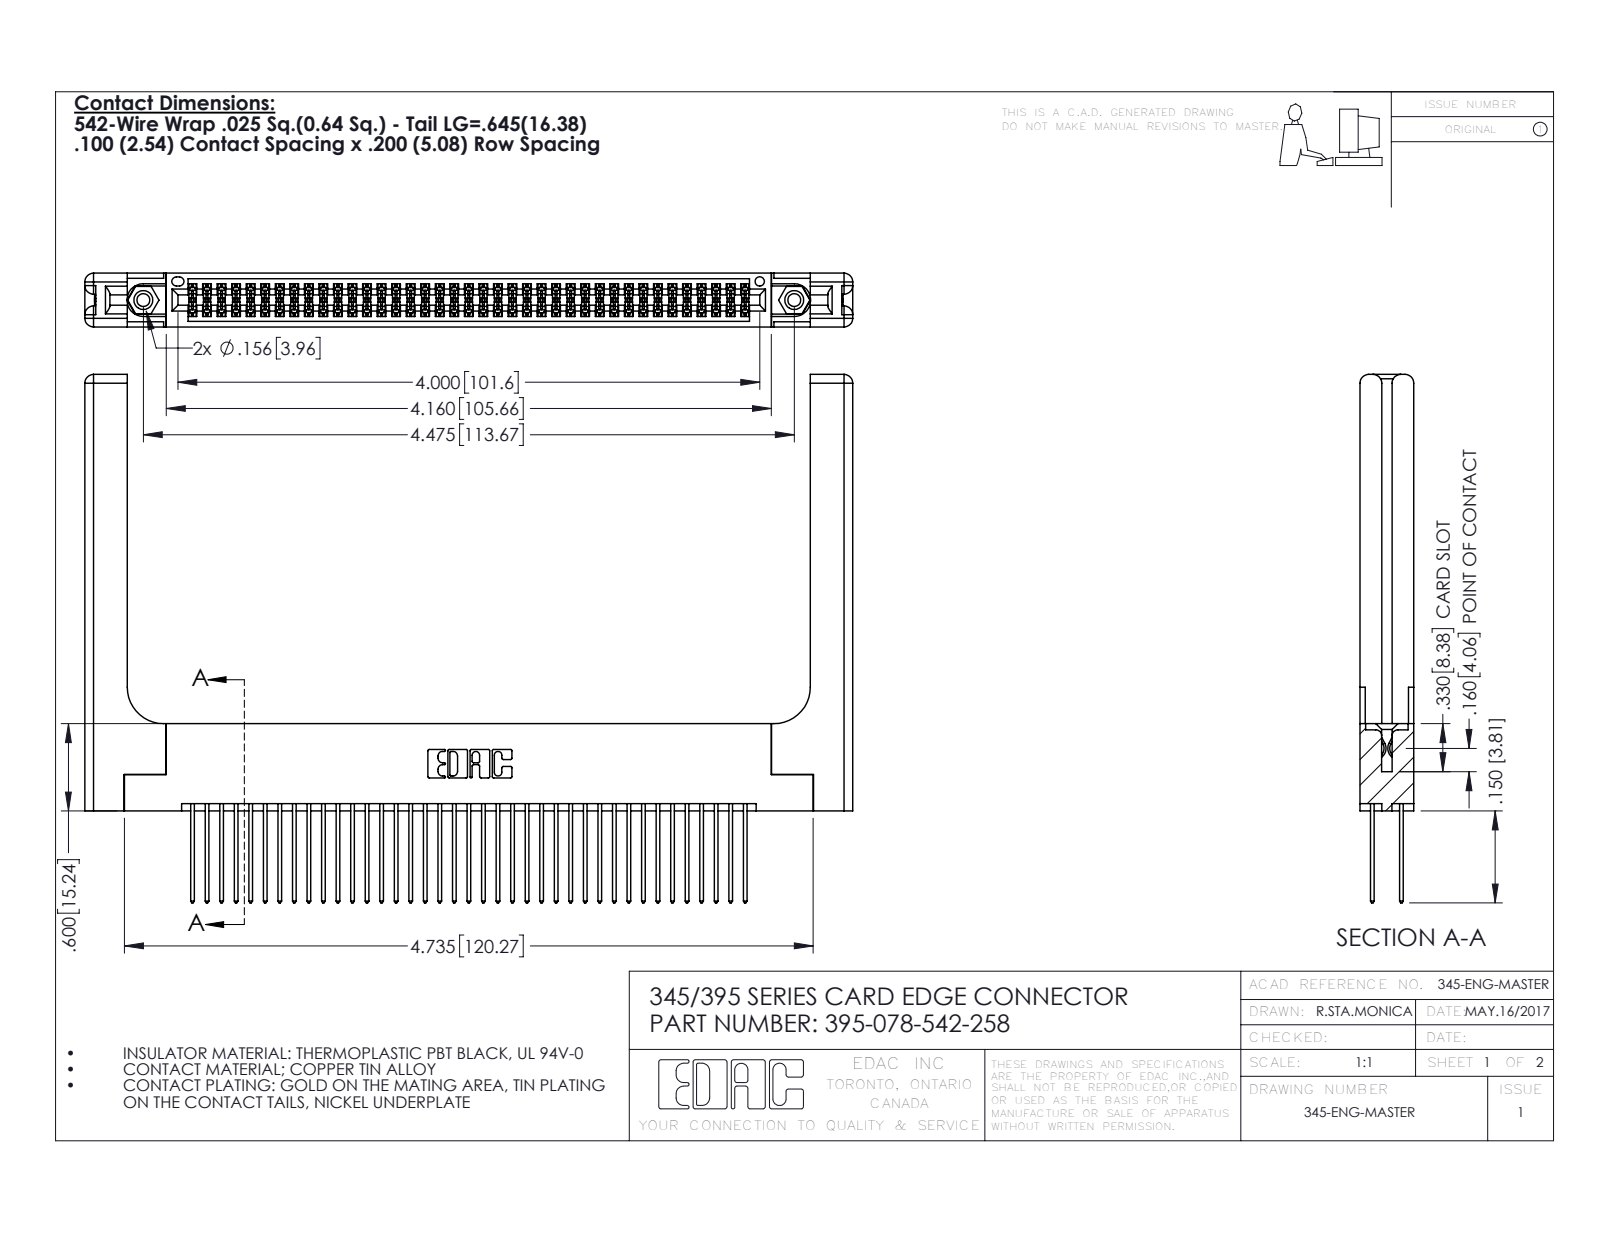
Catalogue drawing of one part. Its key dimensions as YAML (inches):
part_name: "395-078-542-258; 345 Part_Flush Mounting Lugs - 0.156 Dia-TH; 345-292-001_345-293-142; 345-250-001_345-250-001-102 (+1 more)"
step_written_by: "SolidWorks 2016 (CONFIG_CONTROL_DESIGN)"
units: inches
bodies: {solids: 83, faces: 4282, planar: 2802, cylindrical: 1420, other: 60}
overall_size: [5.279, 3.632, 0.37]
volume: 1.333
surface_area: 41
round_holes:
  - {diameter: 0.089, count: 2}
  - {diameter: 0.125, count: 2}
  - {diameter: 0.156, count: 2}
  - {diameter: 0.064, count: 1}
round_bosses_or_shafts:
  - {diameter: 0.155, count: 2}
partial_cylinders:
  - {radius: 0.006, count: 117}
  - {radius: 0.01, count: 78}
  - {radius: 0.01, count: 22}
  - {radius: 0.06, count: 16}
  - {radius: 0.007, count: 6}
  - {radius: 0.031, count: 6}
  - {radius: 0.026, count: 3}
  - {radius: 0.014, count: 2}
face_to_face_distances: [0.072, 0.298, 0.37, 0.2, 0.098, 0.272, 0.025, 0.225, 0.175, 0.148]
hole_center_spacings: [0.27, 4.239, 4.475]
